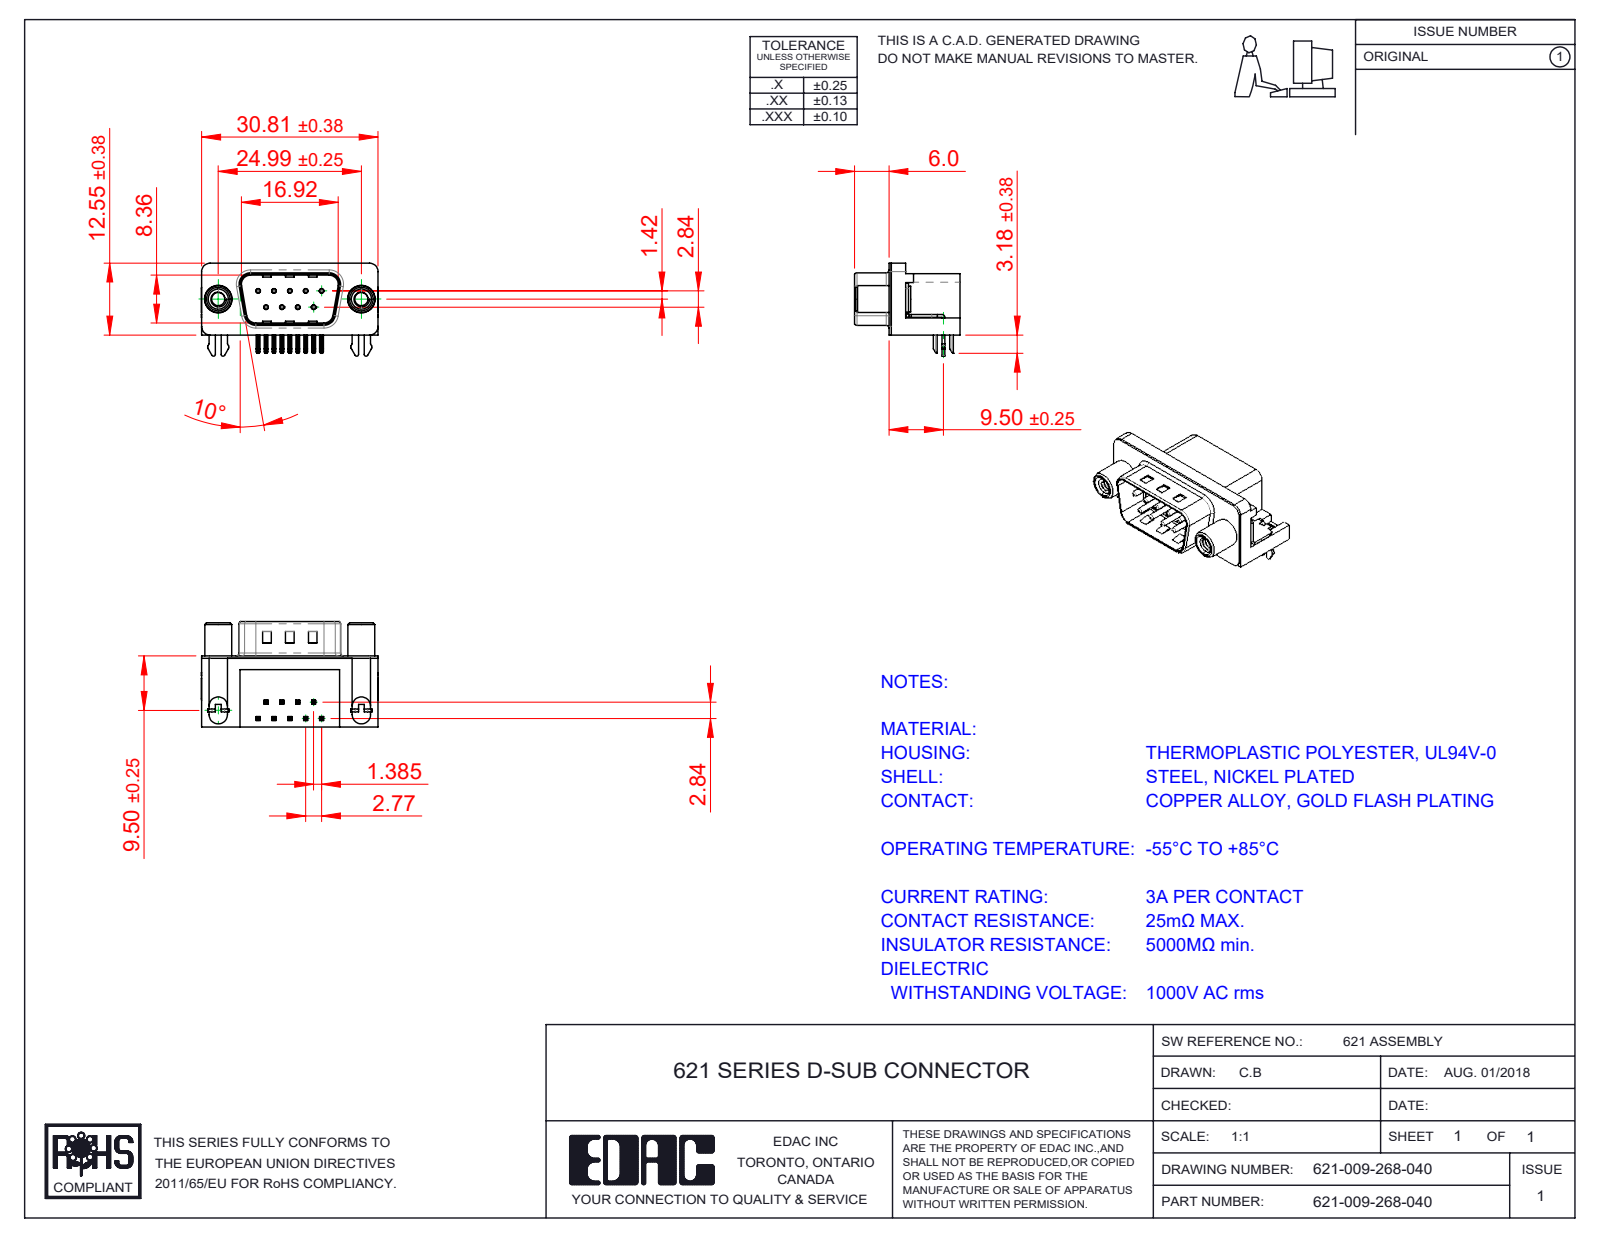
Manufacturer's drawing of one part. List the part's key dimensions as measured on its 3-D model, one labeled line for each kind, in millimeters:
Part name (STEP PRODUCT): 621 Shell_9 Socket; 621 Round Threaded Standoff; 621 4 Prong Board Lock; 621 Contact Top (+3 more)
STEP written by: SolidWorks 2016 (CONFIG_CONTROL_DESIGN)
Units: millimetres
Bodies: 15 solids, 1105 faces (607 planar, 329 cylindrical, 169 other)
Overall size (bounding box): 30.89 × 18.4 × 16.25
Volume: 3 346 mm³ · Surface area: 4 695 mm²
Round holes (diameter × count): ⌀0.35 ×9, ⌀0.8 ×9, ⌀2 ×2, ⌀2.3 ×2, ⌀3.1 ×2, ⌀4 ×2, ⌀4.8 ×2, ⌀5 ×2
Round bosses / shafts (diameter × count): ⌀0.75 ×9, ⌀4.9 ×2, ⌀4.7 ×2, ⌀4.5 ×2, ⌀3.85 ×2, ⌀3 ×2
Partial cylindrical surfaces — rounded edges, fillets, slot ends (radius × count): R0.25 ×40, R0.12 ×18, R1 ×16, R0.5 ×9, R1.5 ×8, R1.6 ×8, R0.9 ×4, R2 ×4
Main face-to-face distances: 0.4, 12, 12.4, 10.35, 9.5, 2.5, 2.9, 2.1, 0.35, 10.7
Hole centre spacings: 3.16, 2.77, 5.54, 5.03, 5.04, 8.31, 7.48, 7.49
